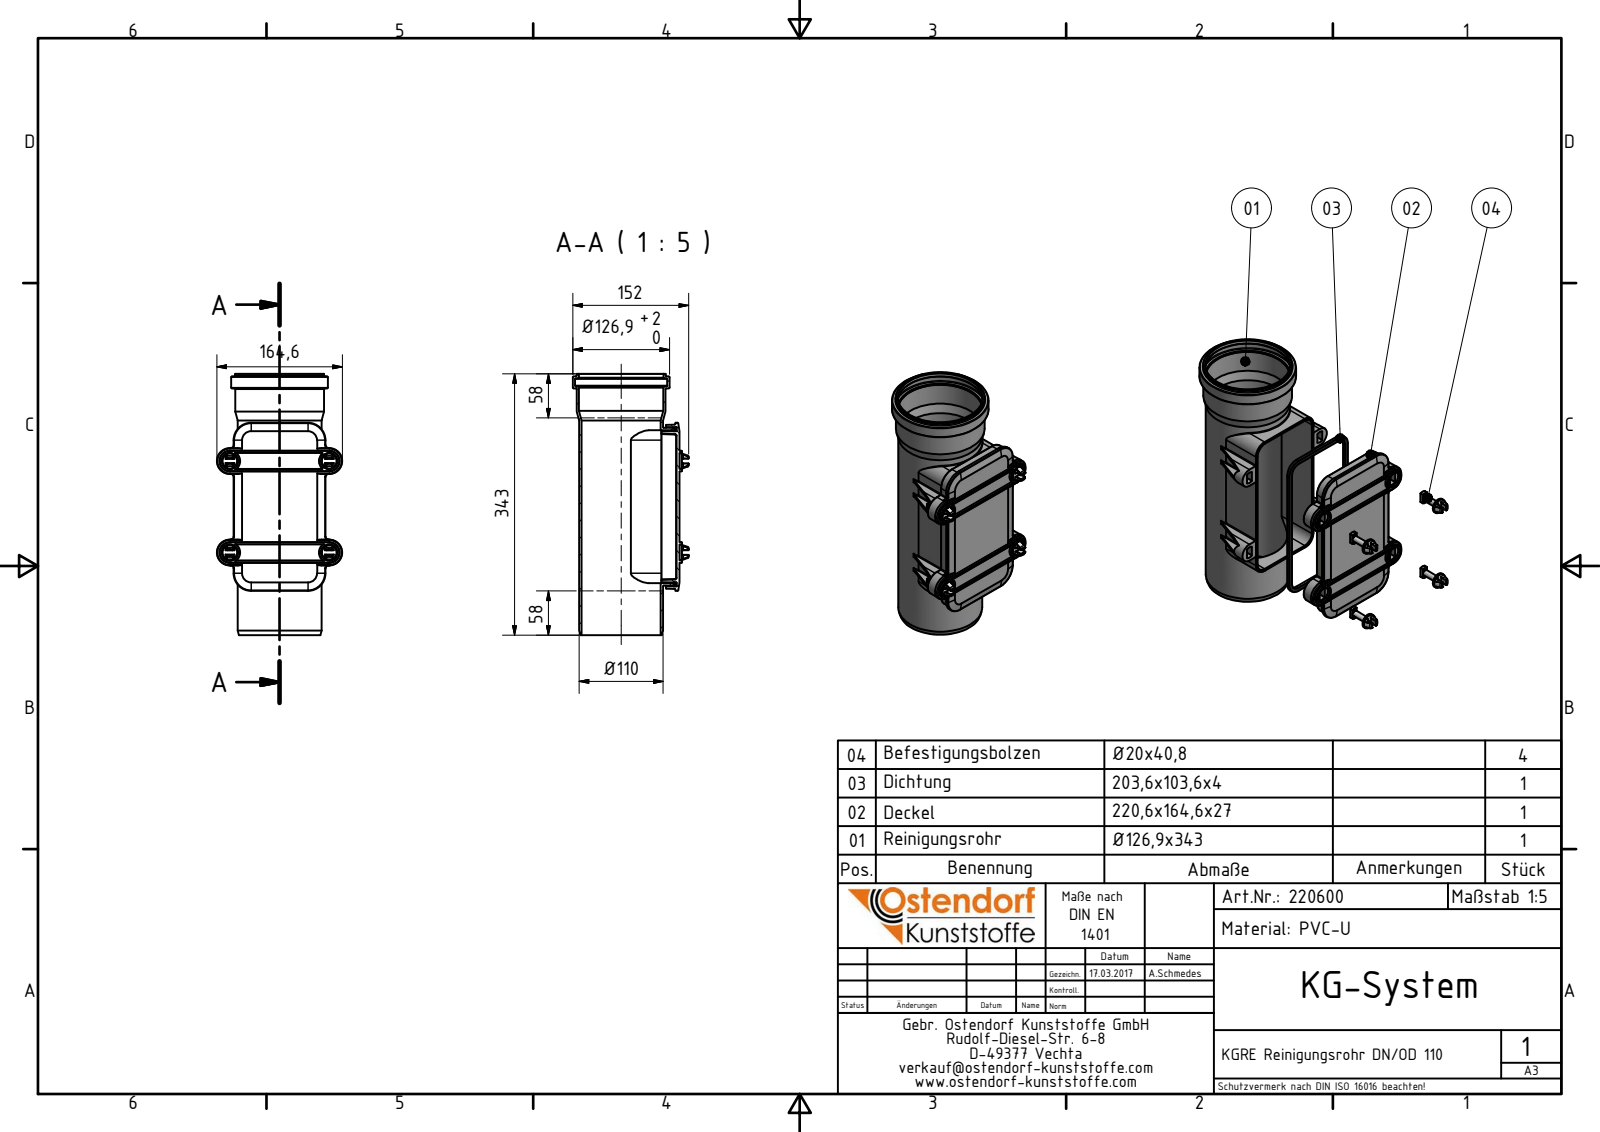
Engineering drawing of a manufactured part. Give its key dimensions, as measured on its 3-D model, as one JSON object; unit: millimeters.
{"part_name": "220600 KGRE Reinigungsrohr eckig DN_OD 110; 220600 KGRE Reinigungsrohr eckig DN_OD 110 Deckel; 220600 KGRE Reinigungsrohr eckig DN_OD 110 Dichtung; 220600 KGRE Reinigungsrohr DN_OD 110 Befestigung (+1 more)", "step_written_by": "Autodesk Inventor 2016 (AUTOMOTIVE_DESIGN)", "units": "millimeters", "bodies": {"solids": 7, "faces": 1264, "planar": 302, "cylindrical": 409, "other": 553}, "overall_size": [343, 164.6, 152], "volume_mm3": 652286, "surface_area_mm2": 395799, "round_holes": [[21, 4], [103.8, 1], [110.7, 1], [111, 1], [121.1, 1]], "round_bosses_or_shafts": [[20, 4], [7.9, 4], [126.9, 1], [116.8, 1], [116.5, 1], [110.2, 1]], "partial_cylinders_radius": [[0.5, 116], [1, 54], [4, 16], [13, 10], [0.3, 8], [2, 8], [3.5, 8], [7.95, 4]], "face_to_face_distances": [4, 3.2, 103.8, 100.6, 107, 37.97, 66.24, 28.27, 8, 120], "hole_center_spacings": [120, 130.6, 177.36]}
